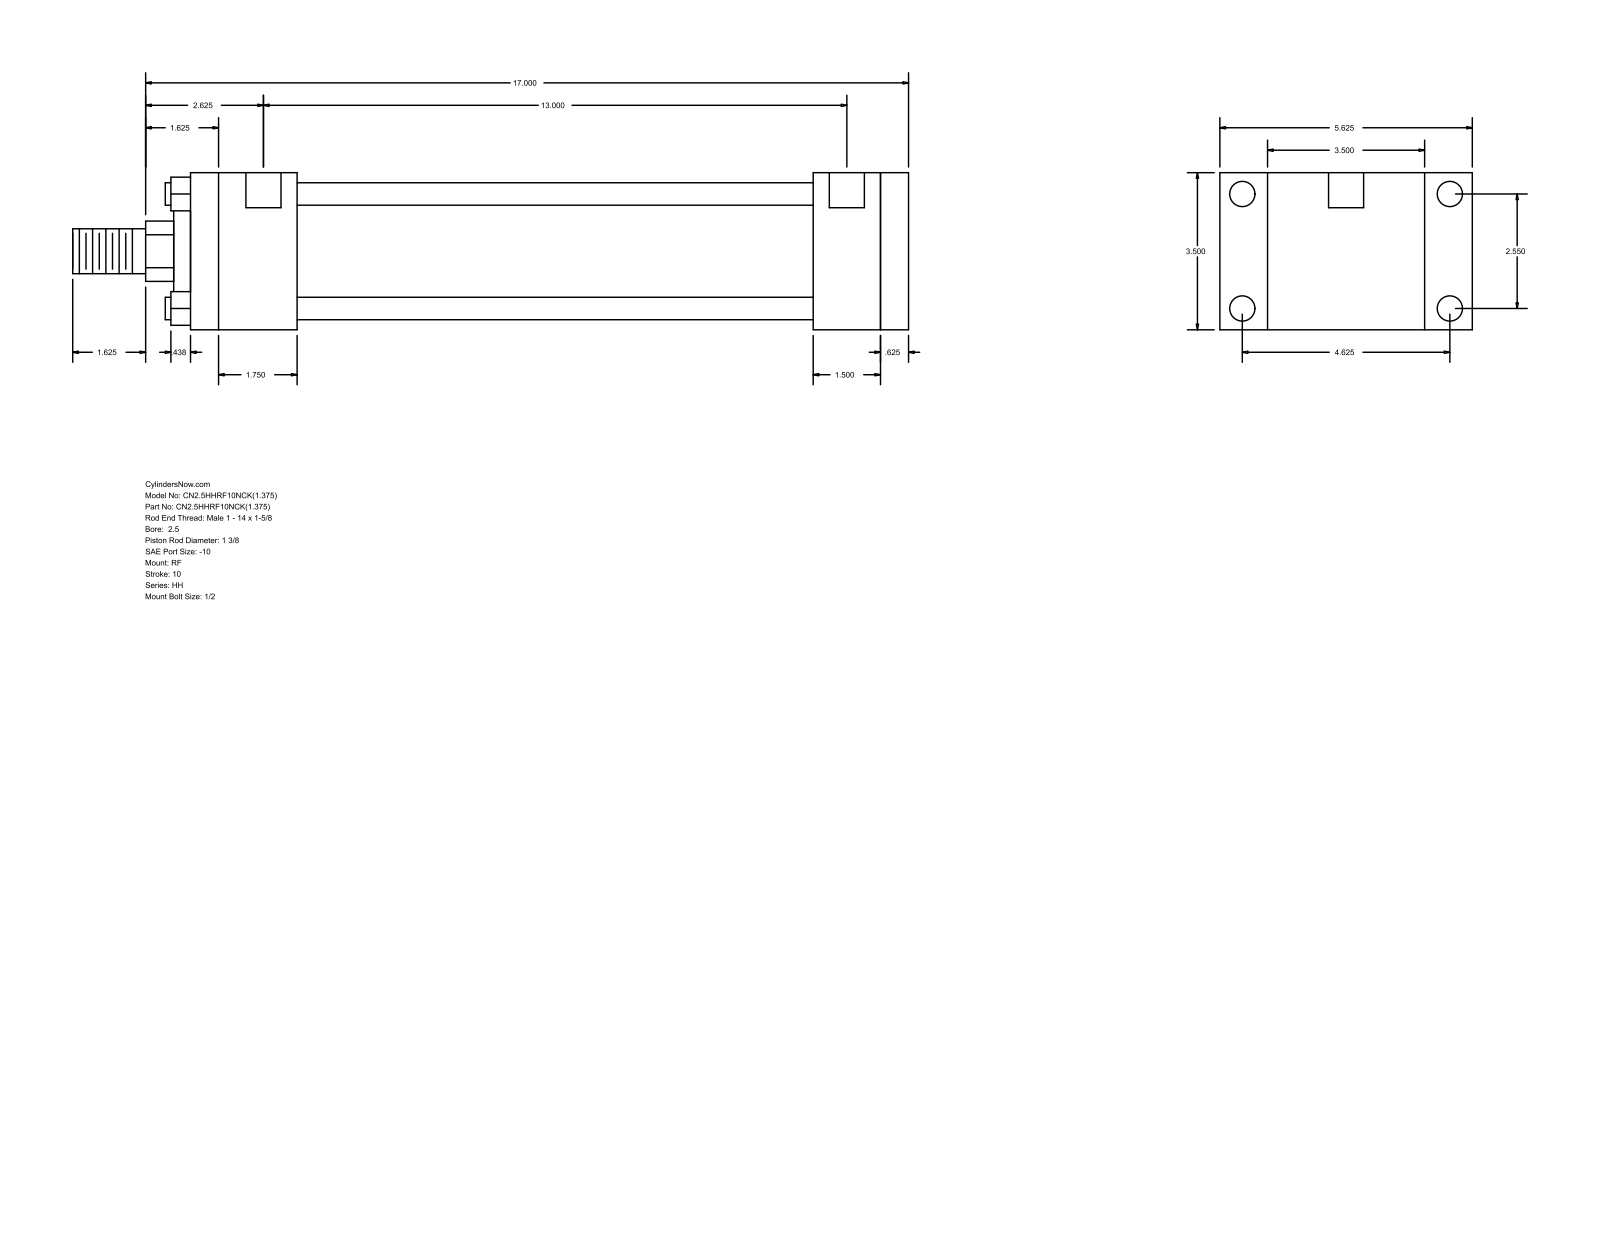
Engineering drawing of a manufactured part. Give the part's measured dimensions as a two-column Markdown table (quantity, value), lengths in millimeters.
| quantity | value |
| --- | --- |
| part name | HH_RF__0250_1.375 |
| STEP written by | GSSL Pune (CONFIG_CONTROL_DESIGN) |
| units | millimeters |
| bodies | 0 solids, 92 faces (64 planar, 28 cylindrical, 0 other) |
| overall size | 473.07 × 142.88 × 88.9 |
| round holes (diameter × count) | 5.56 × 4, 14.3 × 4, 19.84 × 2 |
| round bosses / shafts (diameter × count) | 12.7 × 4, 73.03 × 1, 50.8 × 1, 34.92 × 1, 25.4 × 1 |
| partial cylindrical surfaces (radius × count) | 17.06 × 1 |
| main face-to-face distances | 88.9, 406.4, 390.53, 15.87, 60.32, 330.21, 346.08, 352.42, 292.1, 38.11 |
| hole center spacings | 1.58, 64.76, 117.48, 134.15, 331.79, 333.37, 330.21 |
